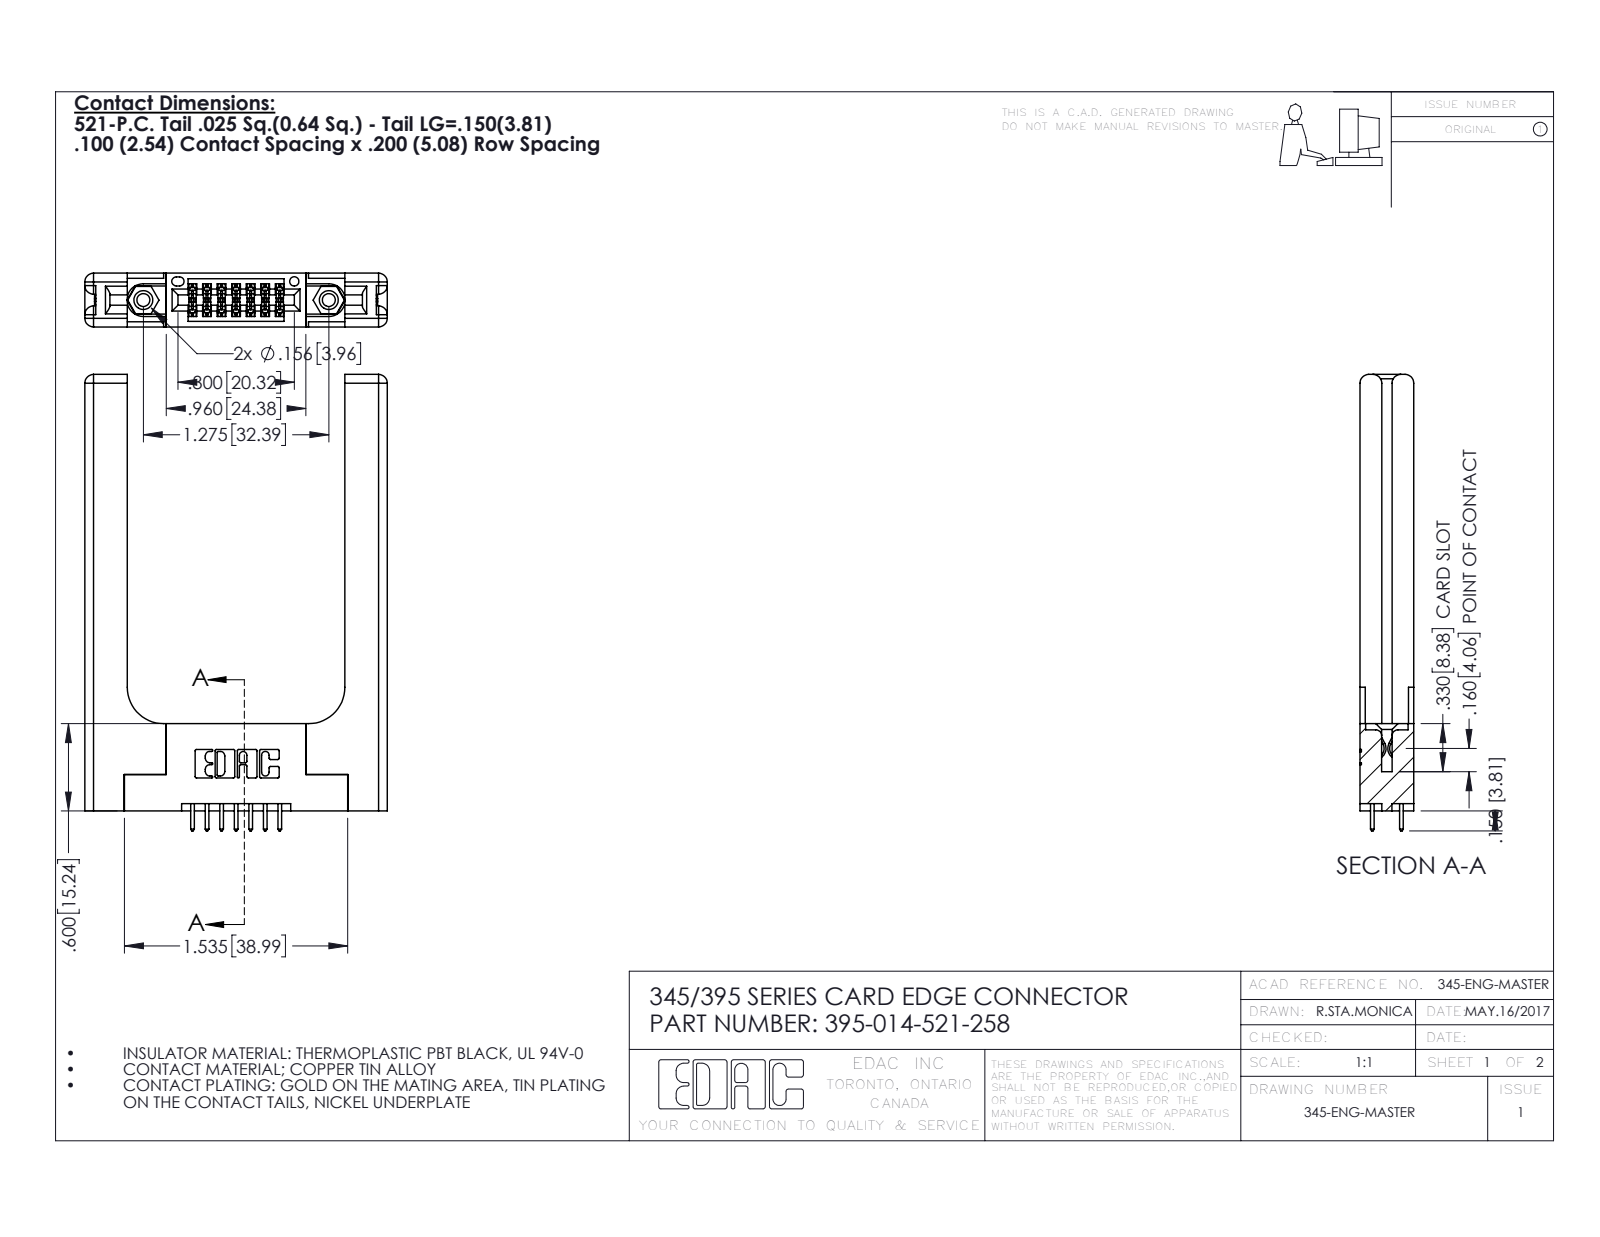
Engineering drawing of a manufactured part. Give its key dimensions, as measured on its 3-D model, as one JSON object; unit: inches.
{"part_name": "345-292-001_345-293-121; 395-014-521-258; 345-250-001_345-250-001-102; 345-220-058_345-220-058 (+1 more)", "step_written_by": "SolidWorks 2016 (CONFIG_CONTROL_DESIGN)", "units": "inches", "bodies": {"solids": 19, "faces": 1082, "planar": 690, "cylindrical": 332, "other": 60}, "overall_size": [3.137, 2.079, 0.37], "volume_in3": 0.81, "surface_area_in2": 17.73, "round_holes": [[0.089, 2], [0.125, 2], [0.156, 2], [0.064, 1]], "round_bosses_or_shafts": [[0.155, 2]], "partial_cylinders_radius": [[0.01, 22], [0.006, 21], [0.06, 16], [0.01, 14], [0.007, 6], [0.031, 6], [0.026, 3], [0.014, 2]], "face_to_face_distances": [0.37, 0.15, 0.22, 0.072, 0.077, 0.148, 0.298, 1.496, 0.2, 0.071], "hole_center_spacings": [0.27, 1.045, 1.275]}
